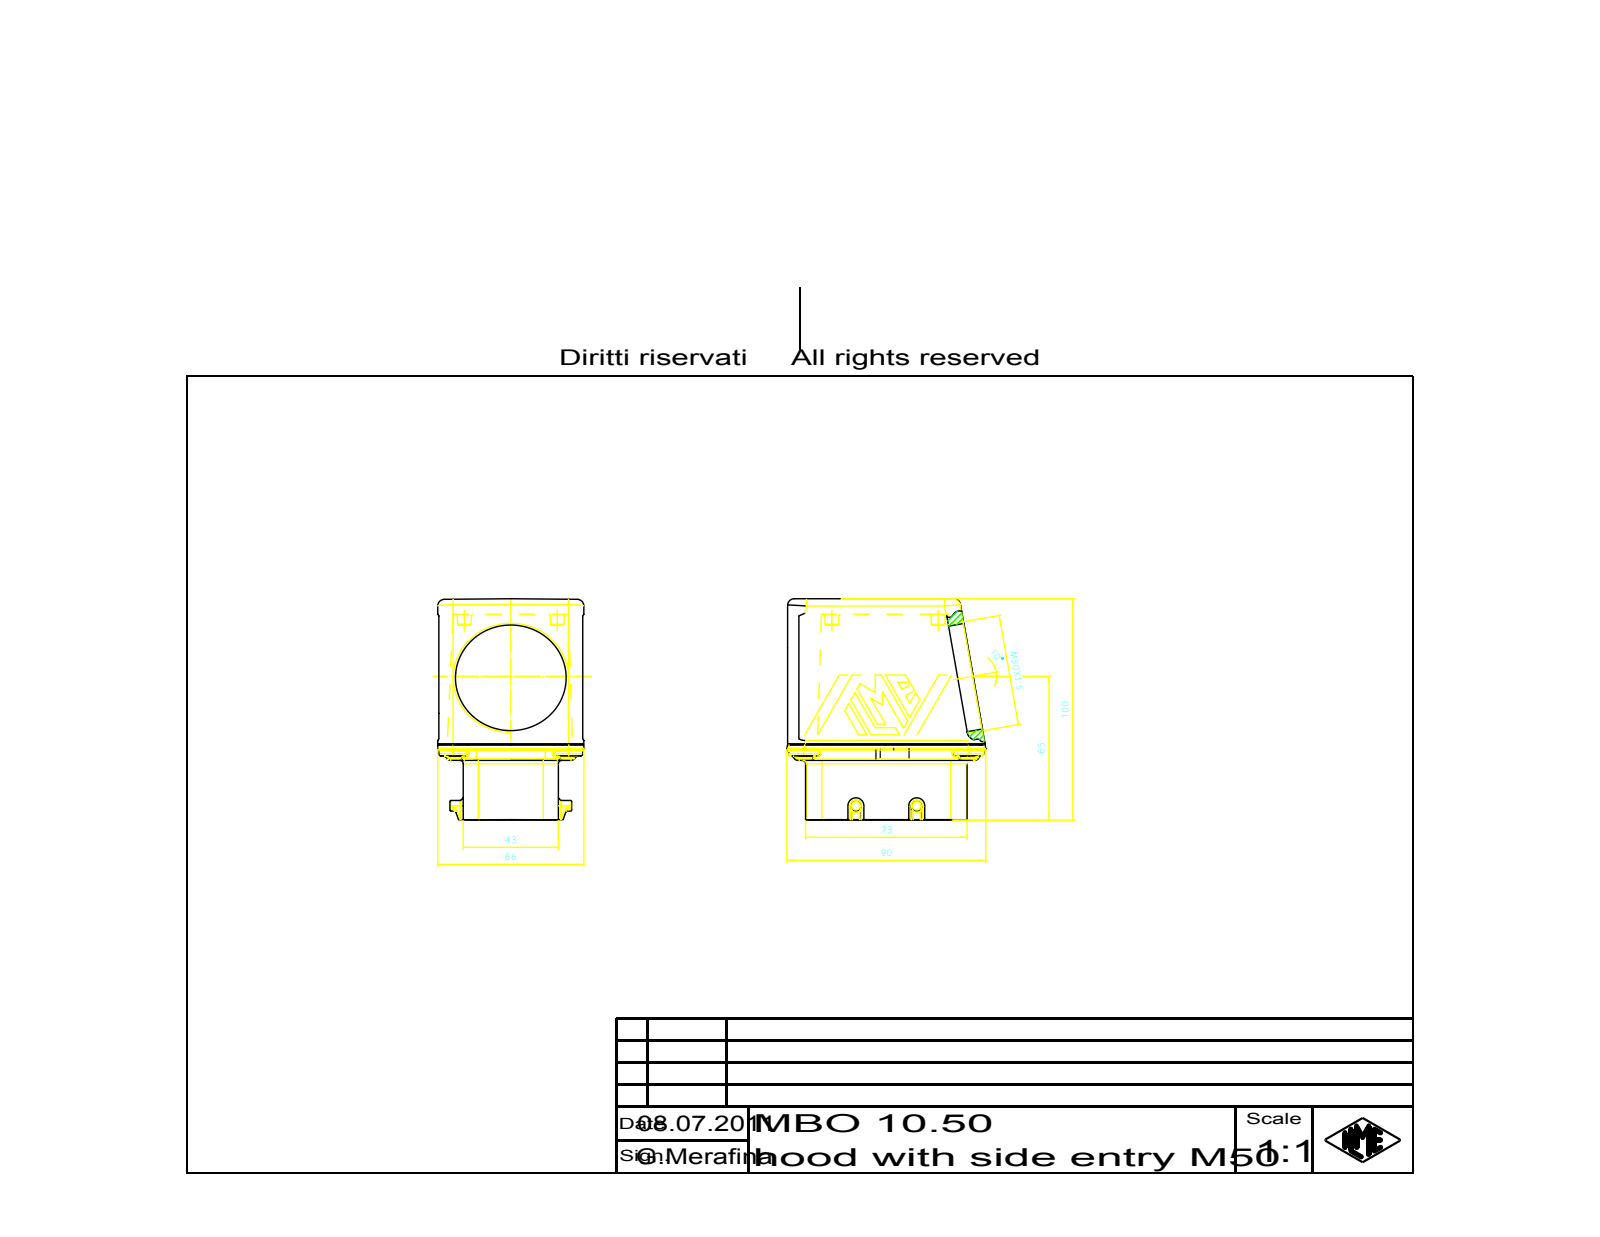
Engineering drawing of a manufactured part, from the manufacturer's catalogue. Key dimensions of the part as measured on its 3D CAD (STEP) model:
Part name (STEP PRODUCT): 53848_Body_1_Body_1.1
STEP written by: CoCreate Modeling 16.00A 16-Aug-2008 (C) Parametric Technology GmbH (AUTOMOTIVE_DESIGN)
Units: millimetres
Bodies: 1 solid, 609 faces (297 planar, 148 cylindrical, 164 other)
Overall size (bounding box): 99.49 × 88.76 × 66.01
Volume: 360 273 mm³ · Surface area: 47 706 mm²
Round holes (diameter × count): ⌀50 ×1
Round bosses / shafts (diameter × count): ⌀4.8 ×2
Partial cylindrical surfaces — rounded edges, fillets, slot ends (radius × count): R1 ×46, R0.3 ×18, R7 ×12, R3 ×10, R0.5 ×8, R1.5 ×6, R4.2 ×4, R5 ×4
Main face-to-face distances: 72.73, 65.01, 0.4, 65.41, 25.04, 11, 54.01, 54, 43, 11.01
